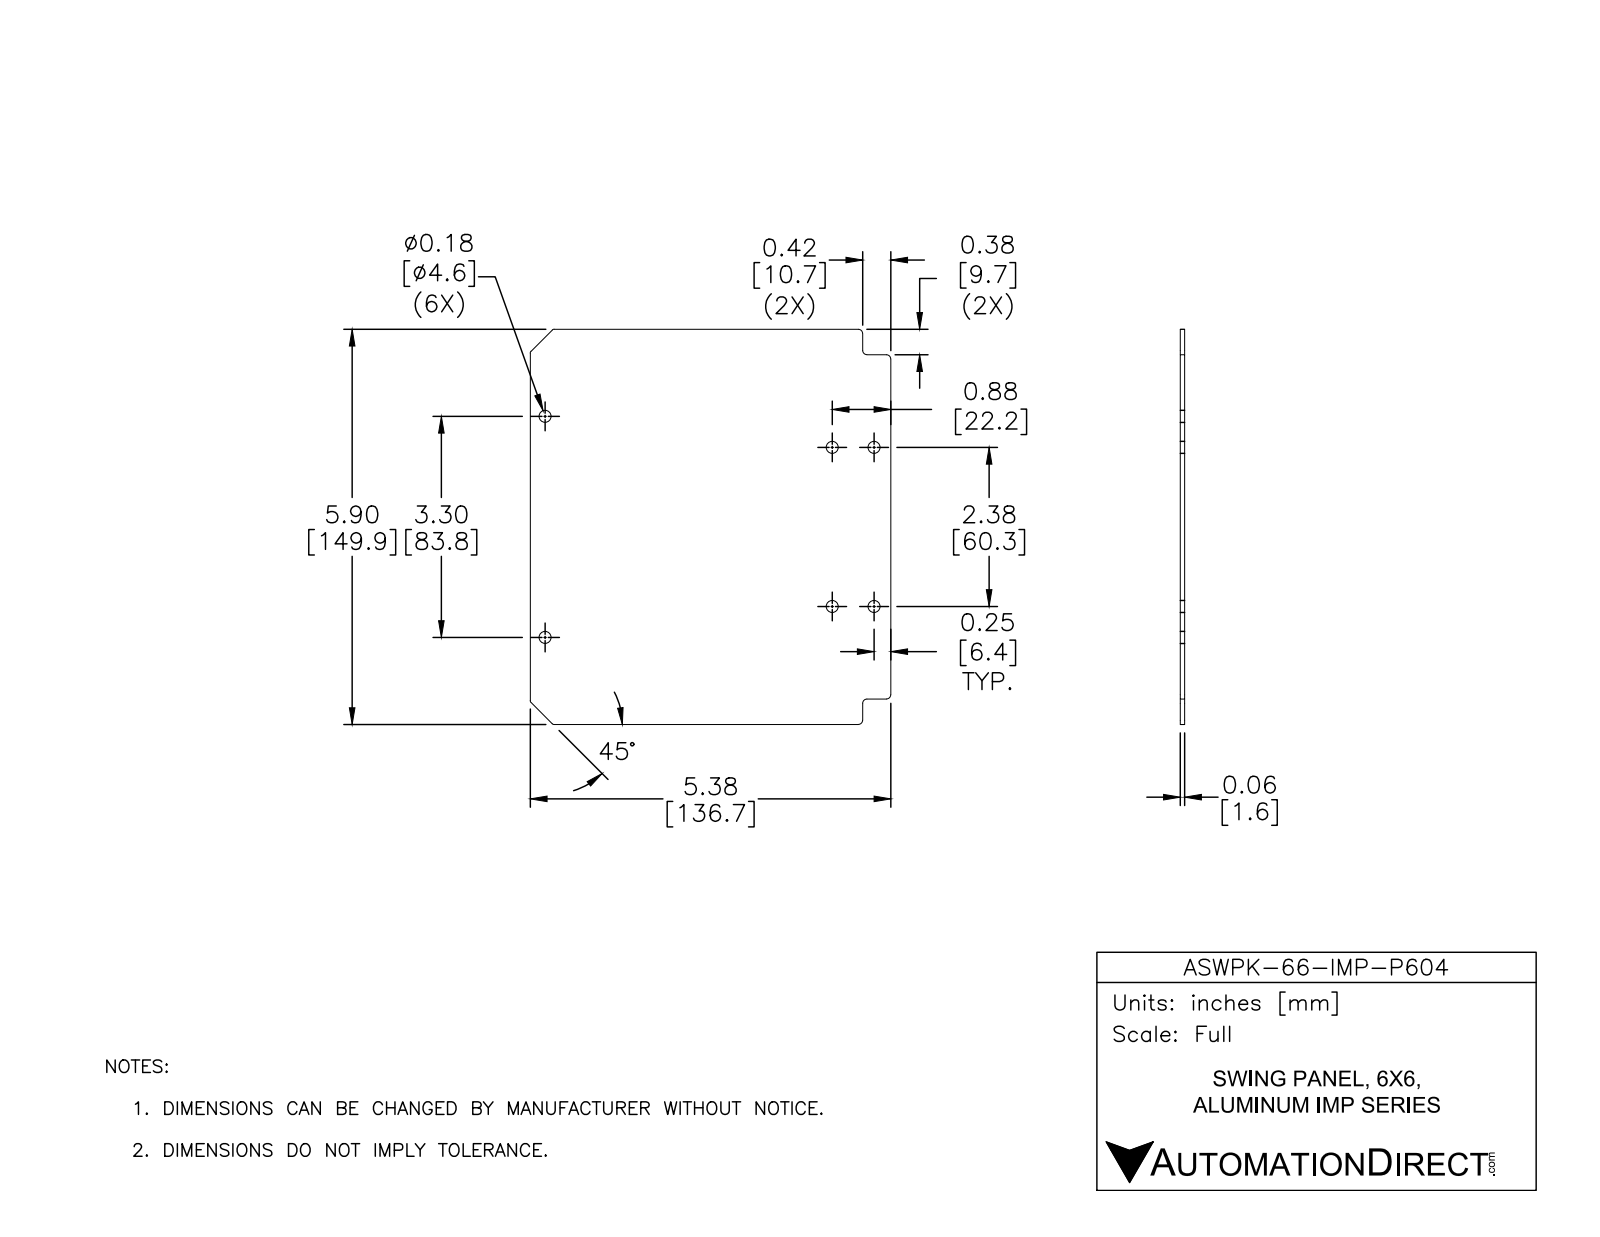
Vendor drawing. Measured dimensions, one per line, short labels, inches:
name: ASWPK-66-IMP-P604
written by: SolidWorks 2016 (AUTOMOTIVE_DESIGN)
unit: in
bodies: 1 solid, 34 faces (12 planar, 22 cylindrical, 0 other)
size: 5.9 × 5.383 × 0.064
volume: 1.998 in³; area: 63.97 in²
holes: 6× ⌀0.18
rounds: 6× R0.063, 4× R0.04
face distances: 0.064, 5.383, 5.9, 0.38, 5.52, 4.963, 0.42, 5.14
hole spacings: 0.625, 2.375, 2.456, 4.312, 4.934, 5.141, 5.673, 3.3
